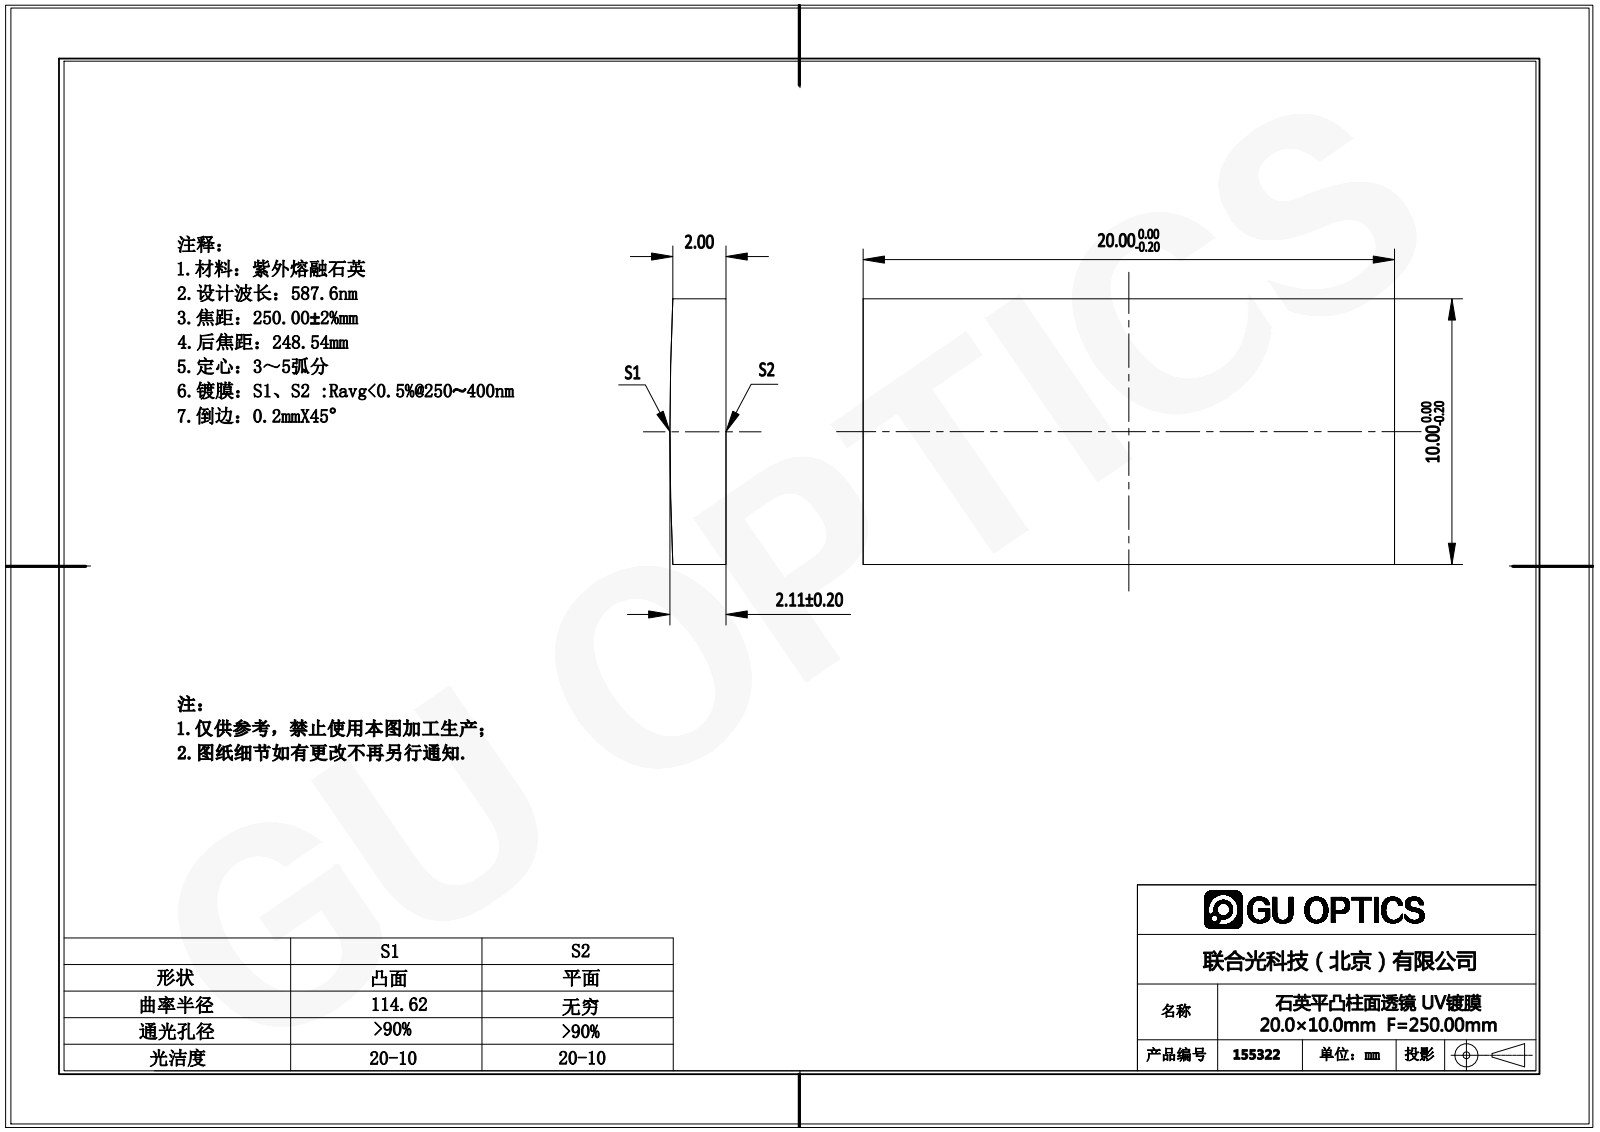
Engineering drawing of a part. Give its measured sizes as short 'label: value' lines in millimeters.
name: 155288
written by: SolidWorks 2016 (AUTOMOTIVE_DESIGN)
unit: mm
bodies: 1 solid, 6 faces (5 planar, 1 cylindrical, 0 other)
size: 20 × 10 × 2.11
volume: 415 mm³; area: 522 mm²
rounds: 1× R114.62
face distances: 10, 20
